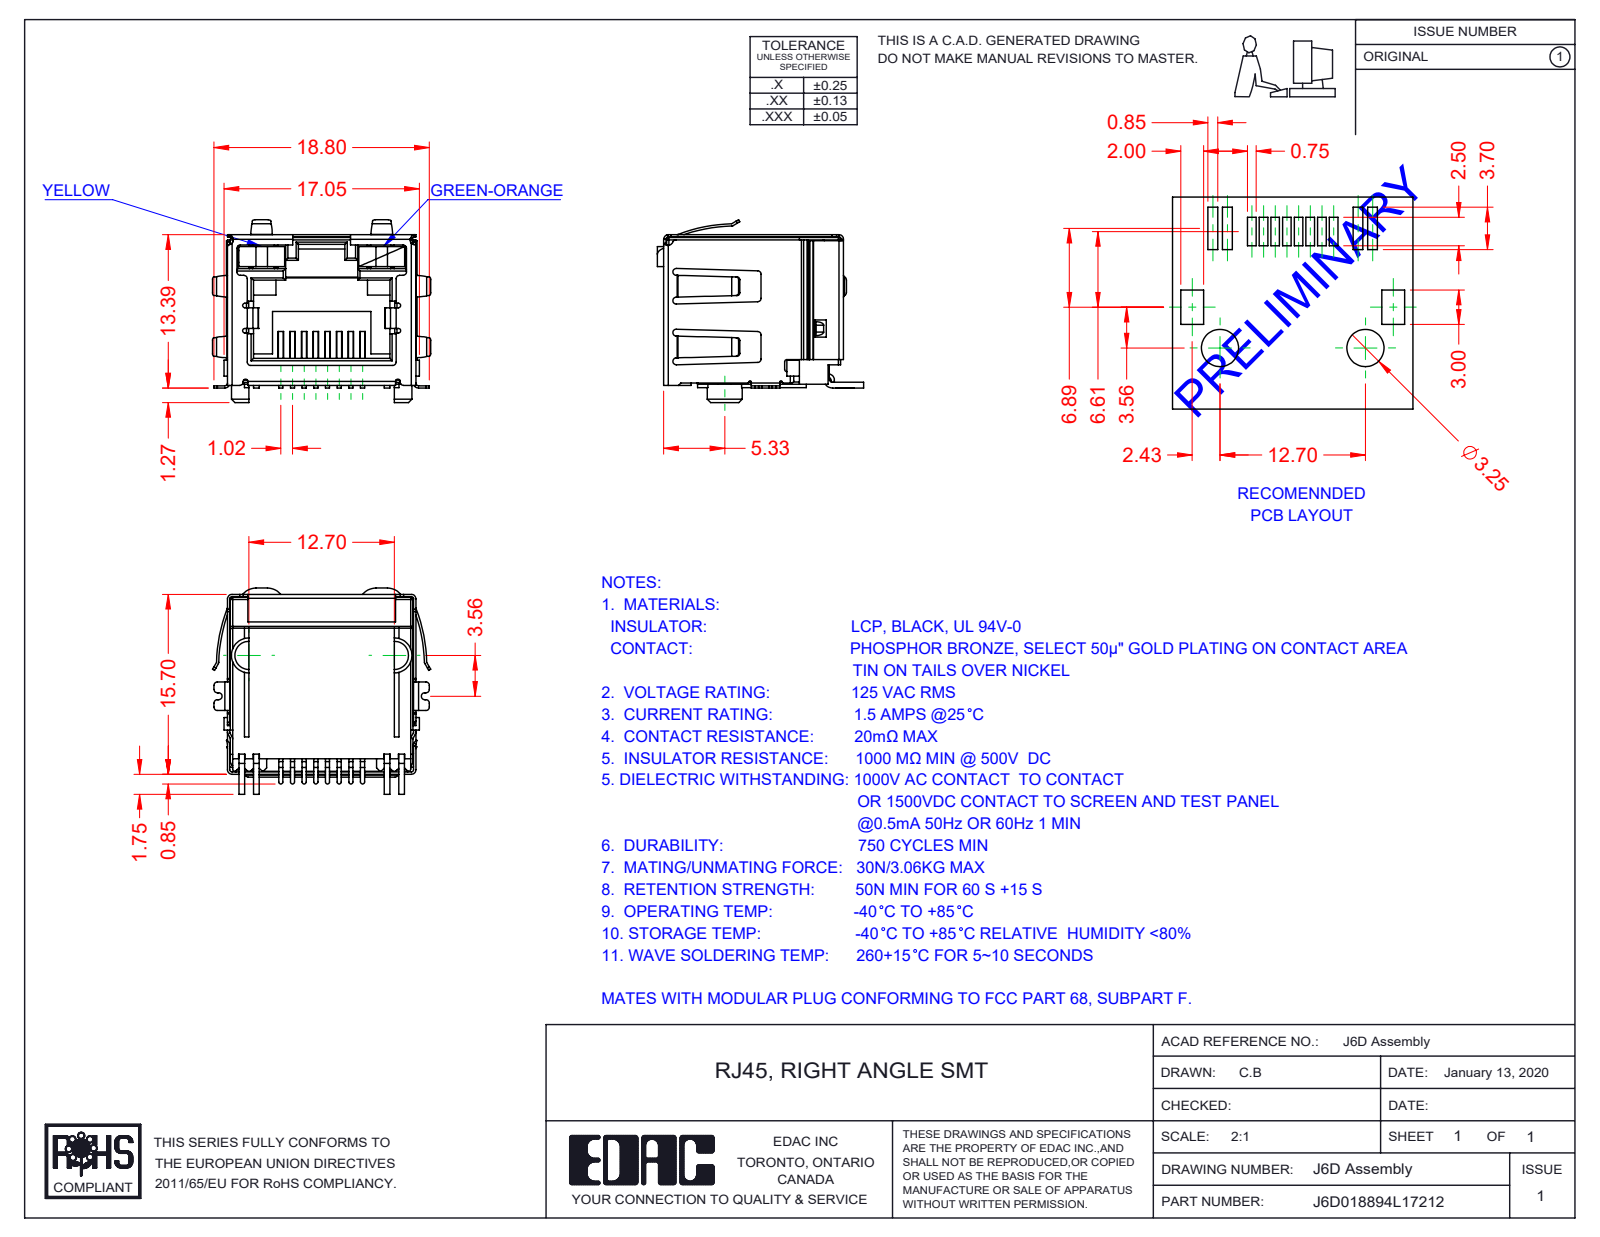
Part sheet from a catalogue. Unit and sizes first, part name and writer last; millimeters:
Units: millimetres
Overall size (bounding box): 19.06 × 18 × 15.95
Partial cylindrical surfaces — rounded edges, fillets, slot ends (radius × count): R0.3 ×55, R0.2 ×40, R0.4 ×19, R0.25 ×16, R0.1 ×12, R0.15 ×8, R0.18 ×8, R0.5 ×6
Main face-to-face distances: 16, 16.2, 16.25, 2.25, 1, 15.95, 12.8, 0.45, 13.05, 10.6
Volume: 1 790 mm³ · Surface area: 4 796 mm²
Bodies: 12 solids, 1031 faces (702 planar, 284 cylindrical, 45 other)
Part name (STEP PRODUCT): 6D Insulator; 6D Contacts; 6D LED RH_7-Green-Orange; J6D018894L17212 (+2 more)
STEP written by: SolidWorks 2016 (CONFIG_CONTROL_DESIGN)
